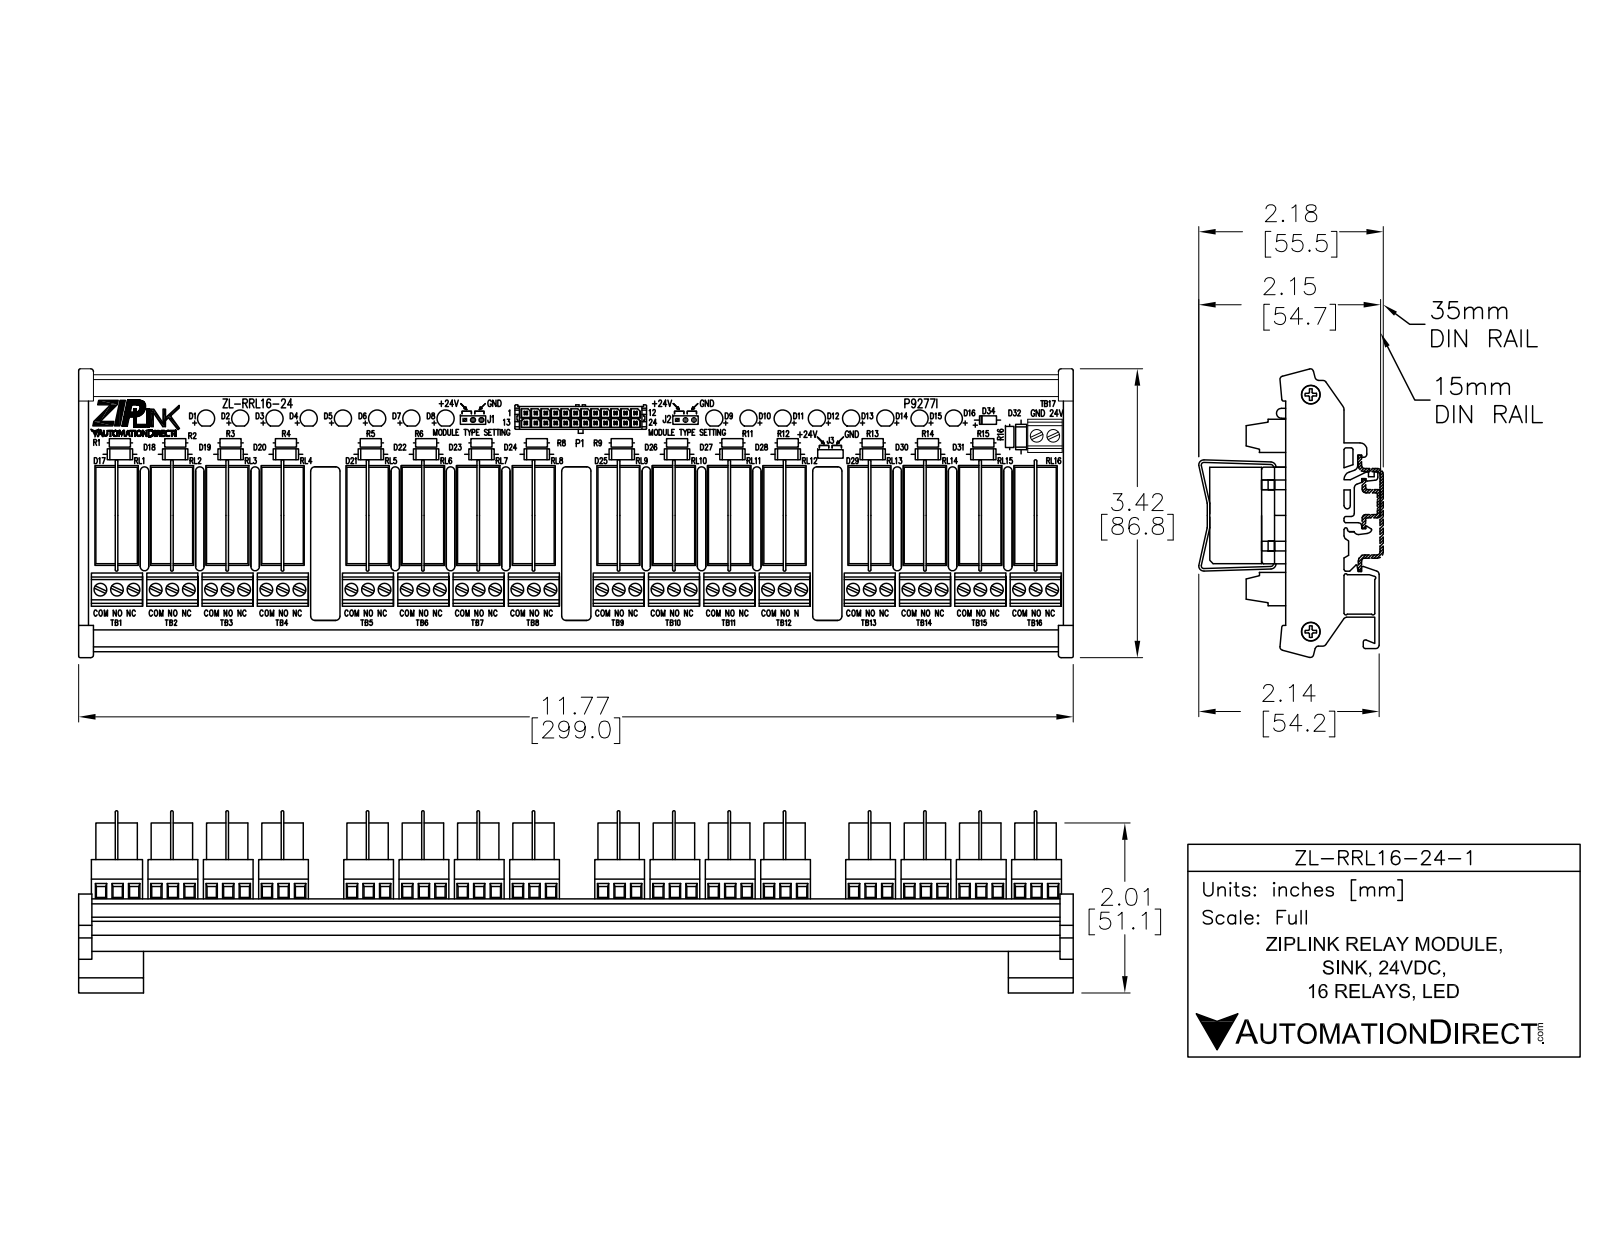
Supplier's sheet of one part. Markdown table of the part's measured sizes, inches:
| quantity | value |
| --- | --- |
| part name | ZL-RRL16-24-1 |
| STEP written by | SolidWorks 2014 (AUTOMOTIVE_DESIGN) |
| units | inches |
| bodies | 21 solids, 2771 faces (1619 planar, 543 cylindrical, 609 other) |
| overall size | 11.819 × 3.42 × 2.184 |
| volume | 20.89 in³ |
| surface area | 280.6 in² |
| round holes (diameter × count) | 0.15 × 50, 0.225 × 3 |
| round bosses / shafts (diameter × count) | 0.08 × 3, 0.19 × 2, 0.1 × 2, 0.205 × 1, 0.199 × 1 |
| partial cylindrical surfaces (radius × count) | 0.02 × 69, 0.015 × 35, 0.03 × 12, 0.06 × 12 |
| main face-to-face distances | 0.434, 0.137, 0.571, 2.97, 0.057, 0.628, 0.491, 0.66, 3.63, 1.32 |
| hole center spacings | 2.97, 0.463, 0.655, 0.192, 2.315, 0.847, 1.31, 1.502 |
